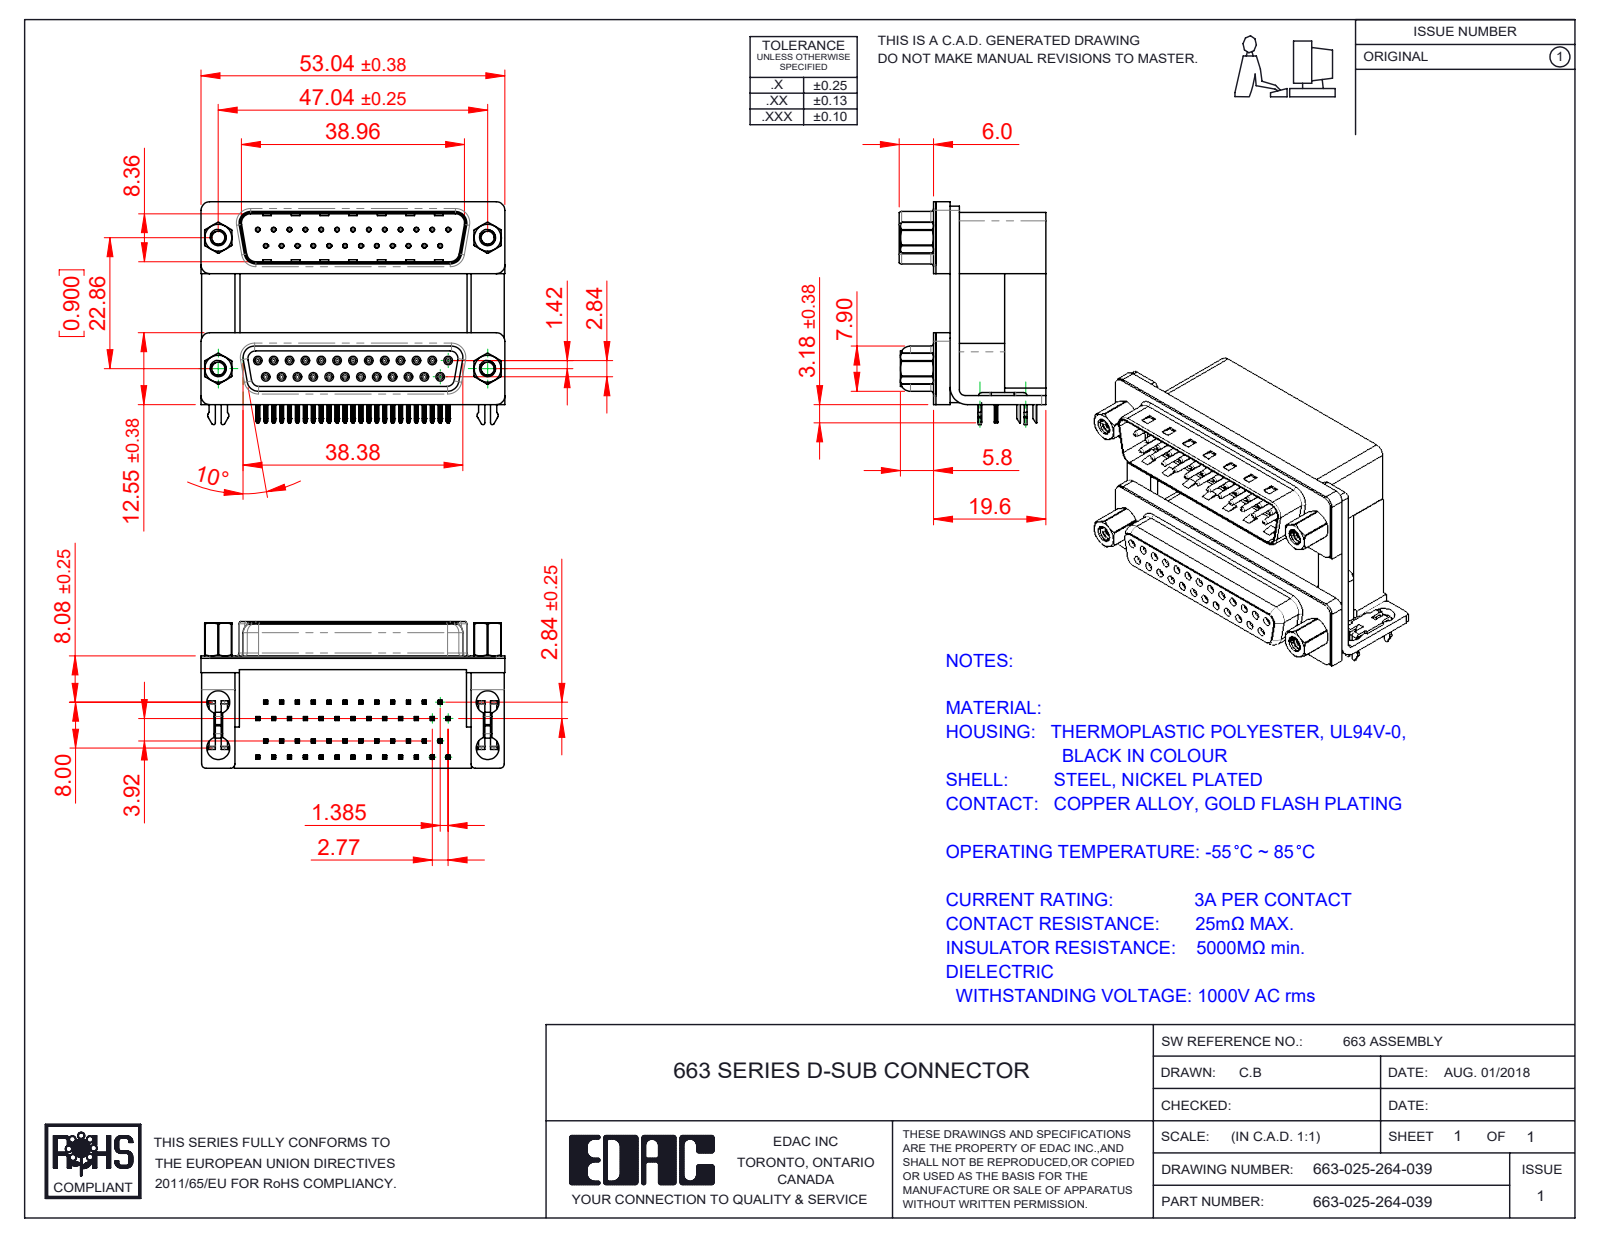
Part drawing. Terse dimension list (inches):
name: 663 Threaded Rivet_4-40; 663-025-264-039; 663 Shell Receptacle_25 Contacts; 663 Contact Bottom Lower (+8 more)
written by: SolidWorks 2020 (CONFIG_CONTROL_DESIGN)
unit: in
bodies: 67 solids, 6607 faces (3403 planar, 1737 cylindrical, 1467 other)
size: 2.088 × 1.532 × 1.008
volume: 1.474 in³; area: 40.53 in²
holes: 50× ⌀0.031, 25× ⌀0.014, 25× ⌀0.035, 8× ⌀0.157, 4× ⌀0.089, 4× ⌀0.09, 4× ⌀0.138, 4× ⌀0.189, 4× ⌀0.197
bosses: 25× ⌀0.047, 25× ⌀0.03, 4× ⌀0.193, 4× ⌀0.187, 4× ⌀0.154, 4× ⌀0.11
rounds: 202× R0.004, 110× R0.01, 100× R0.006, 50× R0.005, 50× R0.014, 25× R0.013, 16× R0.02, 14× R0.059
face distances: 0.756, 0.472, 0.016, 0.283, 0.421, 0.657, 0.374, 0.098, 0.488, 0.9
hole spacings: 0.124, 0.109, 0.218, 0.436, 0.327, 0.198, 0.545, 0.294
